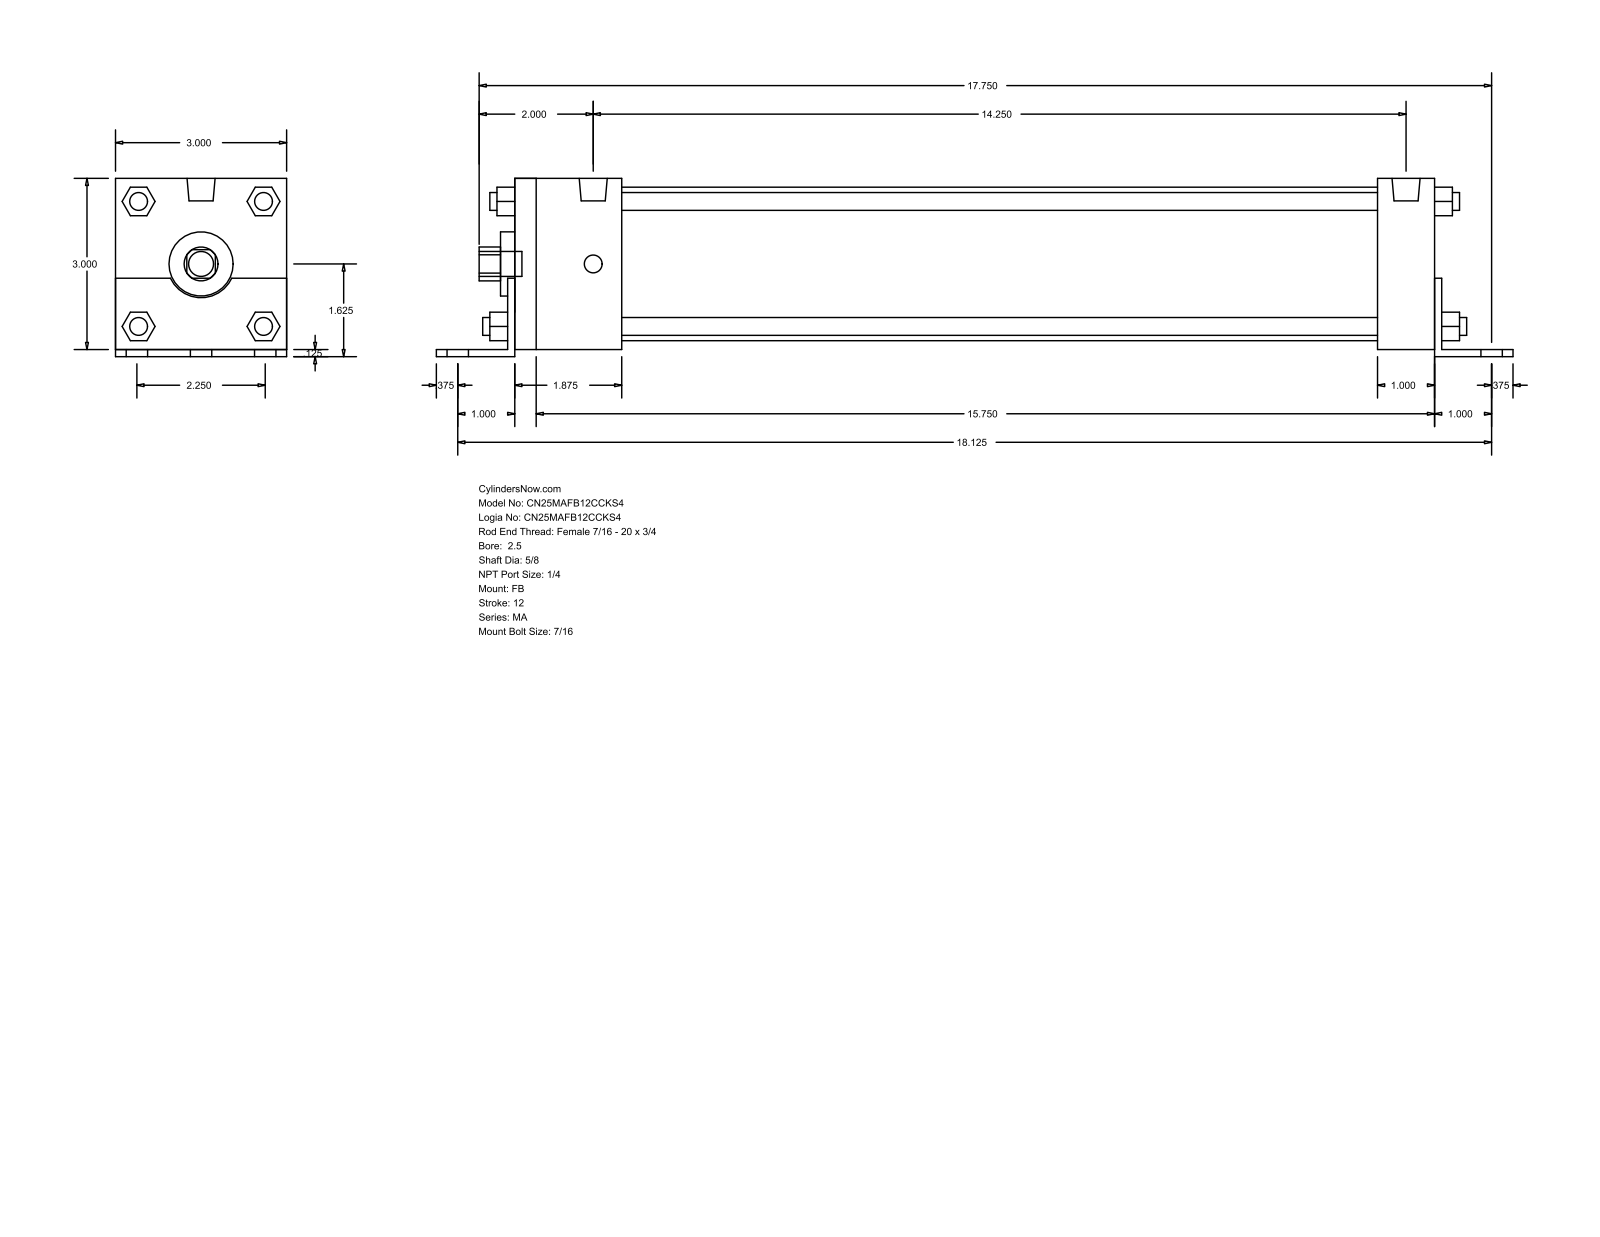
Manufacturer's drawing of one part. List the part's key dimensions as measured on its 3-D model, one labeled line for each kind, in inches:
Part name (STEP PRODUCT): MA_FB__0250_0.625
STEP written by: GSSL Pune (CONFIG_CONTROL_DESIGN)
Units: inches
Bodies: 0 solids, 140 faces (105 planar, 35 cylindrical, 0 other)
Overall size (bounding box): 18.875 × 3.125 × 3
Round holes (diameter × count): ⌀0.625 ×1, ⌀1.125 ×1, ⌀2.69 ×1
Round bosses / shafts (diameter × count): ⌀0.313 ×8, ⌀0.437 ×7, ⌀0.492 ×2
Partial cylindrical surfaces — rounded edges, fillets, slot ends (radius × count): R0.297 ×1, R0.593 ×1
Main face-to-face distances: 3, 0.125, 3.125, 16.125, 16.375, 0.125, 16.25, 1.875, 1, 16.25
